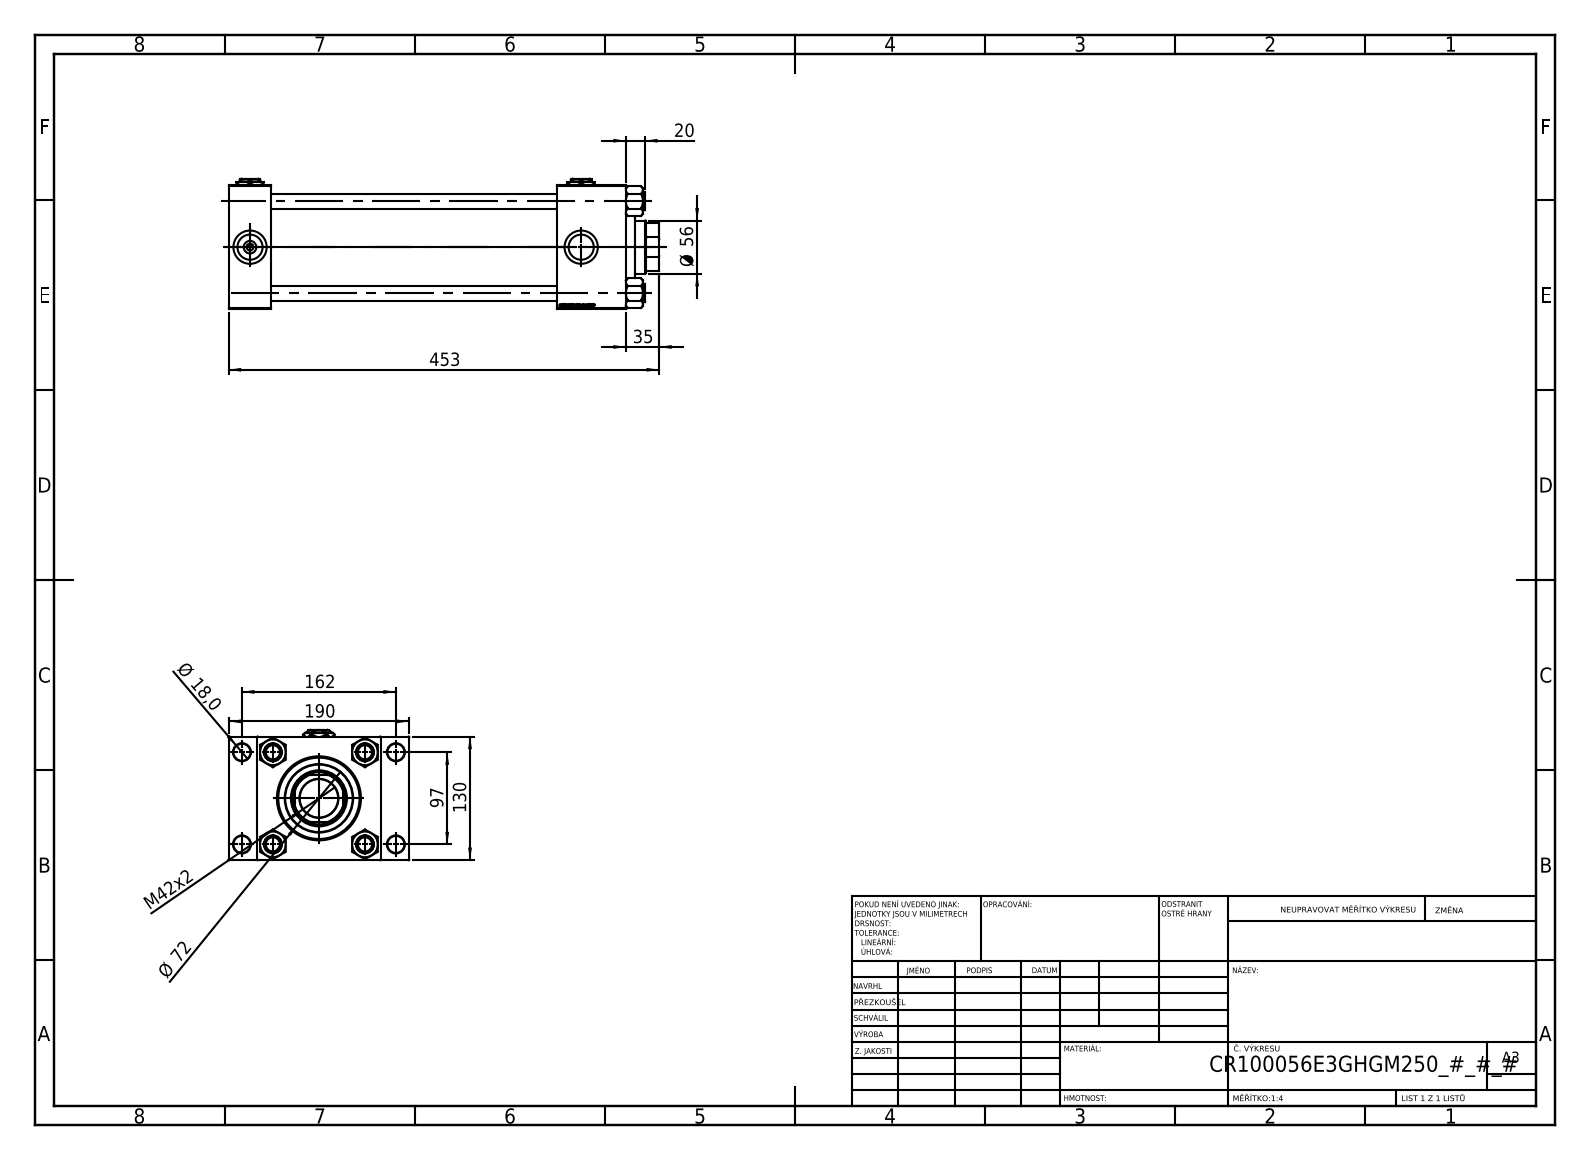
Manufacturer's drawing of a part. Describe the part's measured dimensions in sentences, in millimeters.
The part is named "V215_VC_A; Zatka_pro_OIL_PORT; V215CR_VCP_E; NUT_M5_E (+2 more)". Its 3-D file was written by "SolidWorks 2019 (CONFIG_CONTROL_DESIGN)". It is 13 solids with 1284 faces: 593 planar, 97 cylindrical and 594 other. Overall it measures 453 by 190 by 137 millimeters. Its volume is 3 755 000 cubic millimeters and its surface area 619 866 square millimeters. Round holes: 4 of diameter 16, 4 of diameter 18, 4 of diameter 26.44, 4 of diameter 35, 3 of diameter 7, 1 of diameter 40.5, 1 of diameter 56, 1 of diameter 59, 1 of diameter 76, 1 of diameter 85.5, 1 of diameter 100. Round bosses or shafts: 4 of diameter 19, 1 of diameter 106, 1 of diameter 72. Partial cylindrical surfaces (rounded edges, fillets, slot ends): 1 of radius 27. The main face-to-face distances are 130, 45, 418, 373, 30, 160, 346, 301, 72, 96. The hole center spacings are 32.55, 68.52, 94.41, 96.9, 102.27, 129.45, 161.73, 97.
